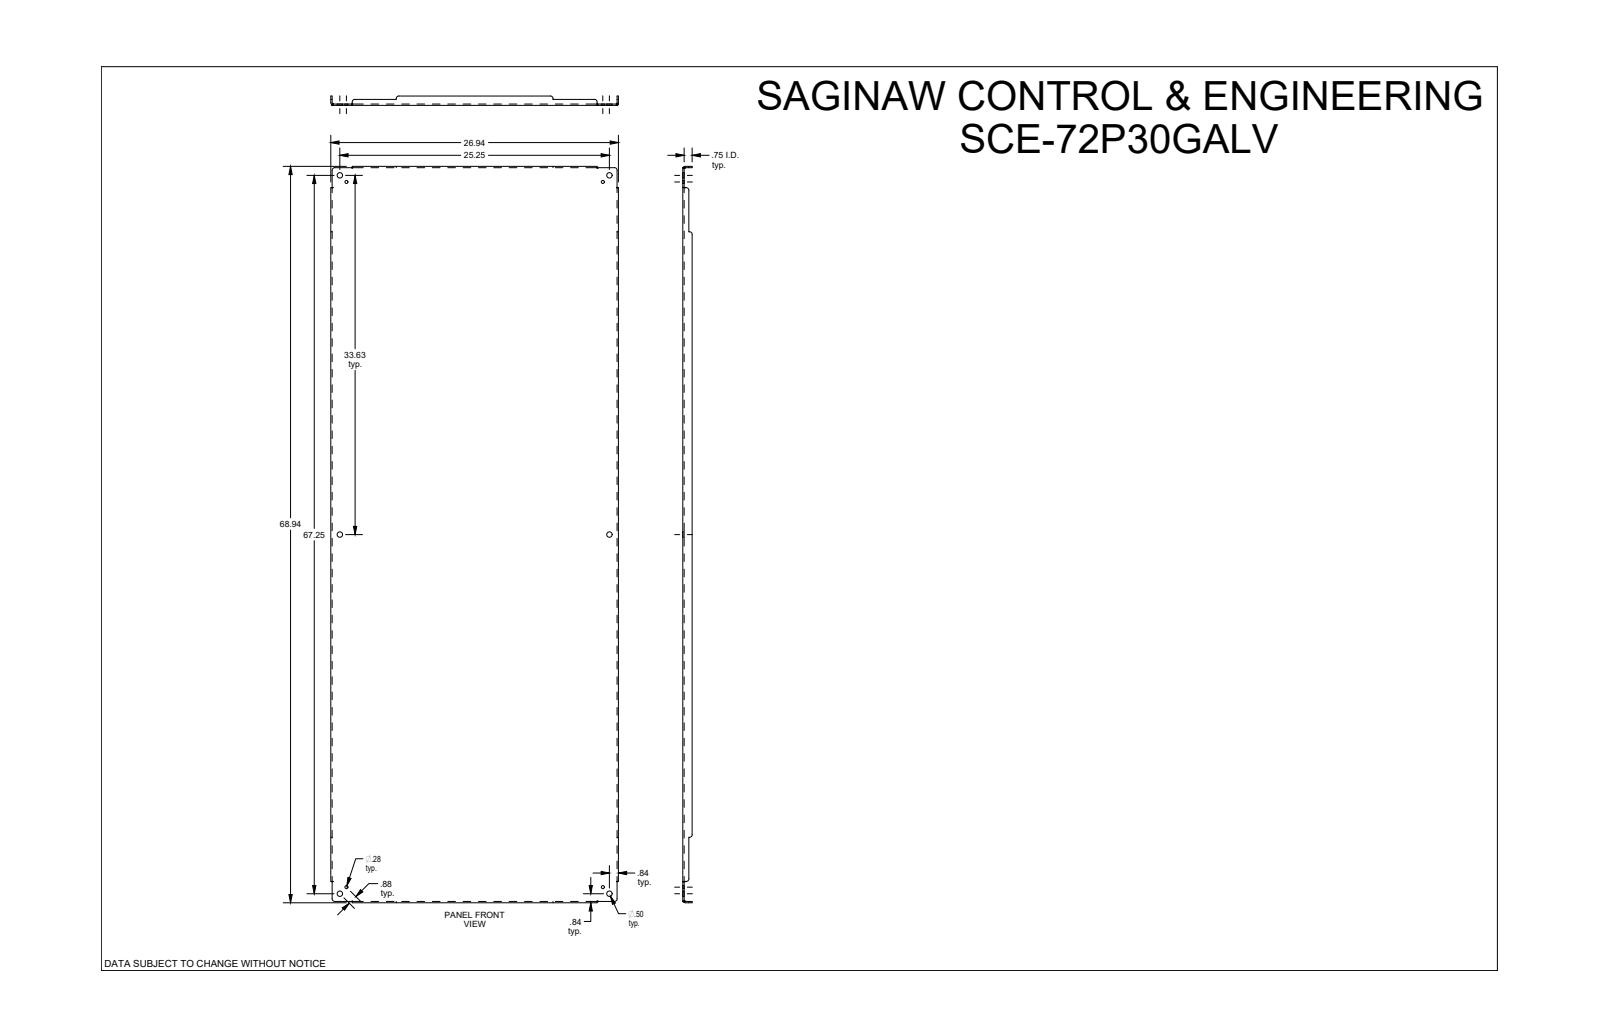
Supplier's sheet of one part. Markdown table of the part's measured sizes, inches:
| quantity | value |
| --- | --- |
| part name | SCE-72P30GALV |
| STEP written by | SolidWorks 2019 (CONFIG_CONTROL_DESIGN) |
| units | inches |
| bodies | 1 solid, 108 faces (46 planar, 38 cylindrical, 24 other) |
| overall size | 68.938 × 26.938 × 0.875 |
| volume | 245.2 in³ |
| surface area | 3 949 in² |
| round holes (diameter × count) | 0.5 × 6, 0.281 × 4 |
| partial cylindrical surfaces (radius × count) | 0.25 × 12, 0.112 × 4, 0.237 × 4 |
| main face-to-face distances | 0.125, 0.125, 26.813, 26.687, 26.938, 68.813, 0.75, 0.875, 68.687, 68.938 |
| hole center spacings | 0.875, 24.639, 33.012, 33.625, 41.184, 42.05, 66.634, 71.038 |
